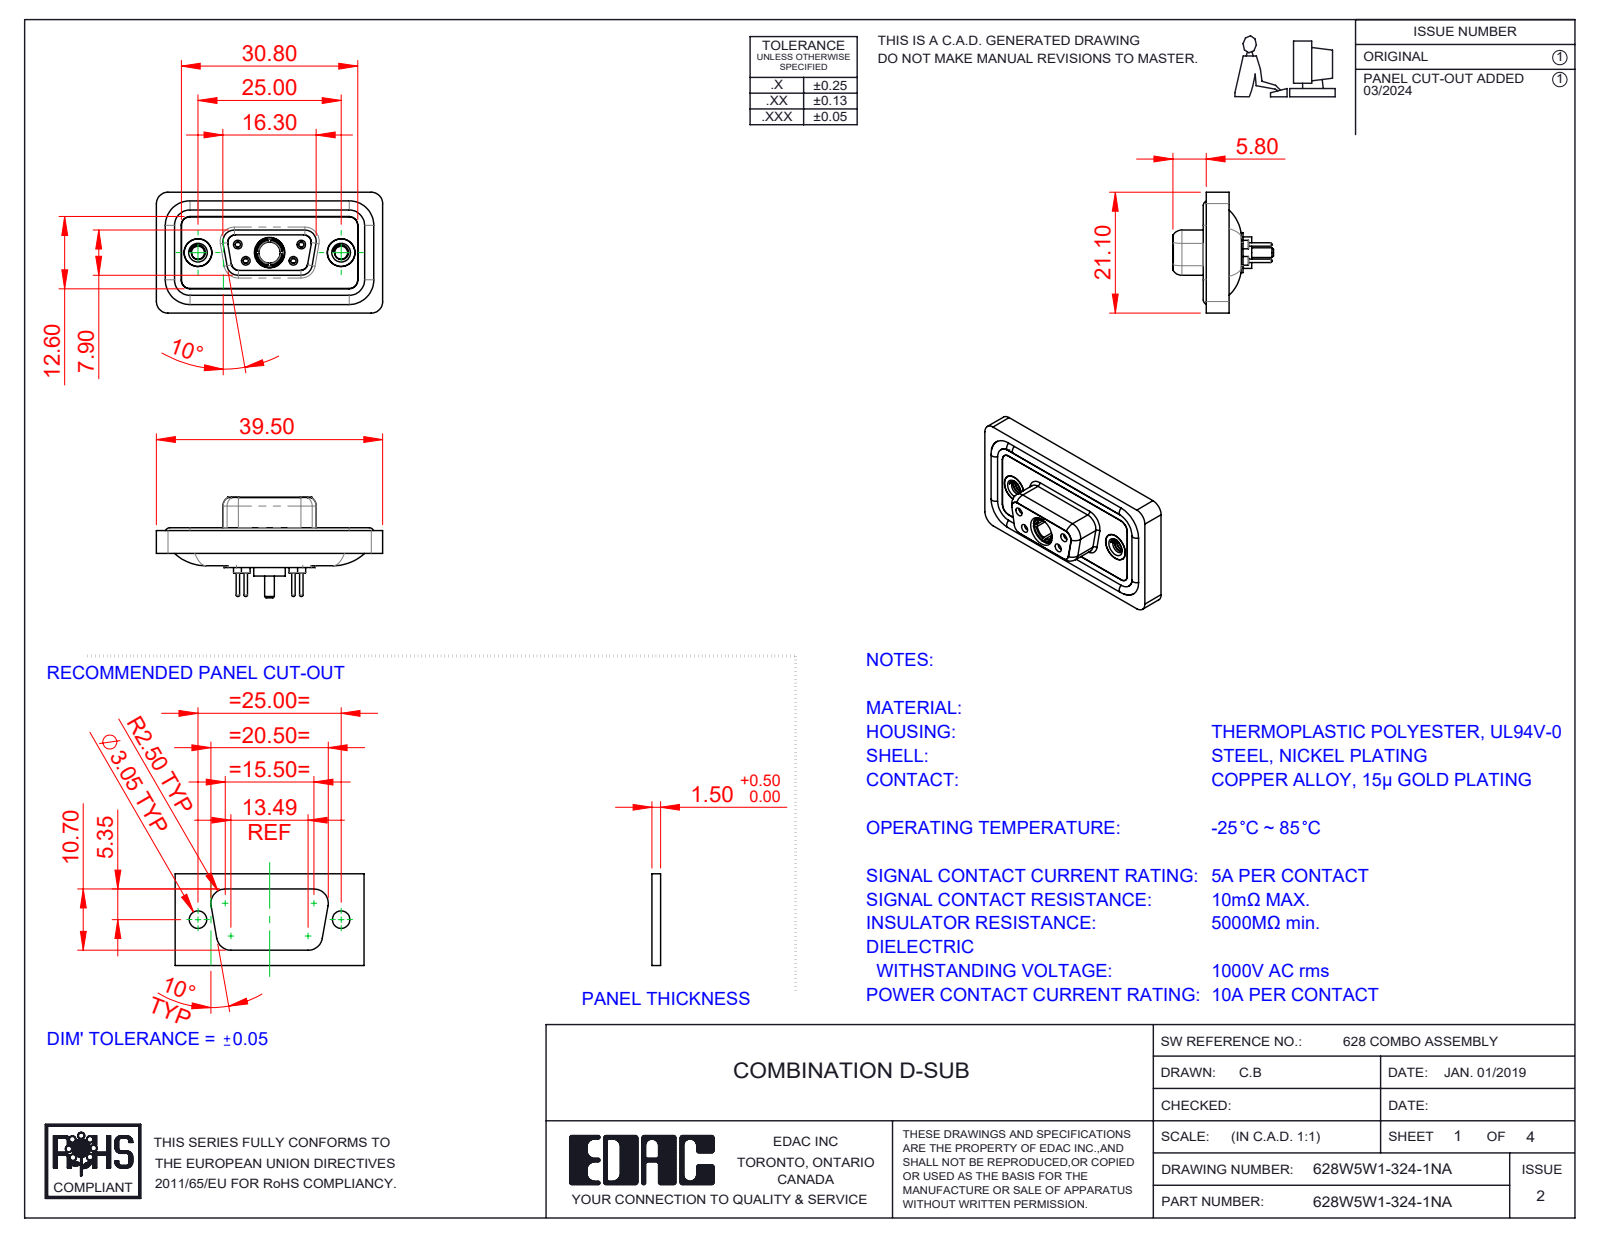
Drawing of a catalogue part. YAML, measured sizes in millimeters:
part_name: "628Combo Shell Rear_09 Contacts; 628Combo Threaded Rivet_A; 628Combo Housing_5W1; 628Combo Shell Front_09 Contacts (+5 more)"
step_written_by: "SolidWorks 2023 (CONFIG_CONTROL_DESIGN)"
units: millimeters
bodies: {solids: 13, faces: 678, planar: 194, cylindrical: 289, other: 195}
overall_size: [39.5, 21.1, 17.55]
volume: 4754
surface_area: 7620
round_holes:
  - {diameter: 0.9, count: 4}
  - {diameter: 1.1, count: 4}
  - {diameter: 1.5, count: 4}
  - {diameter: 2, count: 4}
  - {diameter: 4.85, count: 3}
  - {diameter: 1.6, count: 2}
  - {diameter: 1.7, count: 2}
  - {diameter: 2.26, count: 2}
  - {diameter: 4, count: 2}
  - {diameter: 4.05, count: 2}
  - {diameter: 5, count: 2}
  - {diameter: 3.7, count: 1}
round_bosses_or_shafts:
  - {diameter: 1.6, count: 6}
  - {diameter: 2.2, count: 4}
  - {diameter: 0.6, count: 4}
  - {diameter: 4.95, count: 2}
  - {diameter: 4.8, count: 2}
  - {diameter: 5.5, count: 1}
  - {diameter: 5.2, count: 1}
  - {diameter: 4.96, count: 1}
partial_cylinders:
  - {radius: 1.5, count: 22}
  - {radius: 2, count: 18}
  - {radius: 1.35, count: 8}
  - {radius: 1.6, count: 8}
  - {radius: 0.25, count: 4}
  - {radius: 0.5, count: 4}
  - {radius: 0.6, count: 4}
  - {radius: 0.65, count: 4}
face_to_face_distances: [0.4, 2.9, 1.8, 1.1, 1.6, 0.5, 5.65, 7.45, 5.35, 6.6]
hole_center_spacings: [3.16, 5.72, 7.1, 12.5, 18.1, 4.39, 4.4, 8.31]
